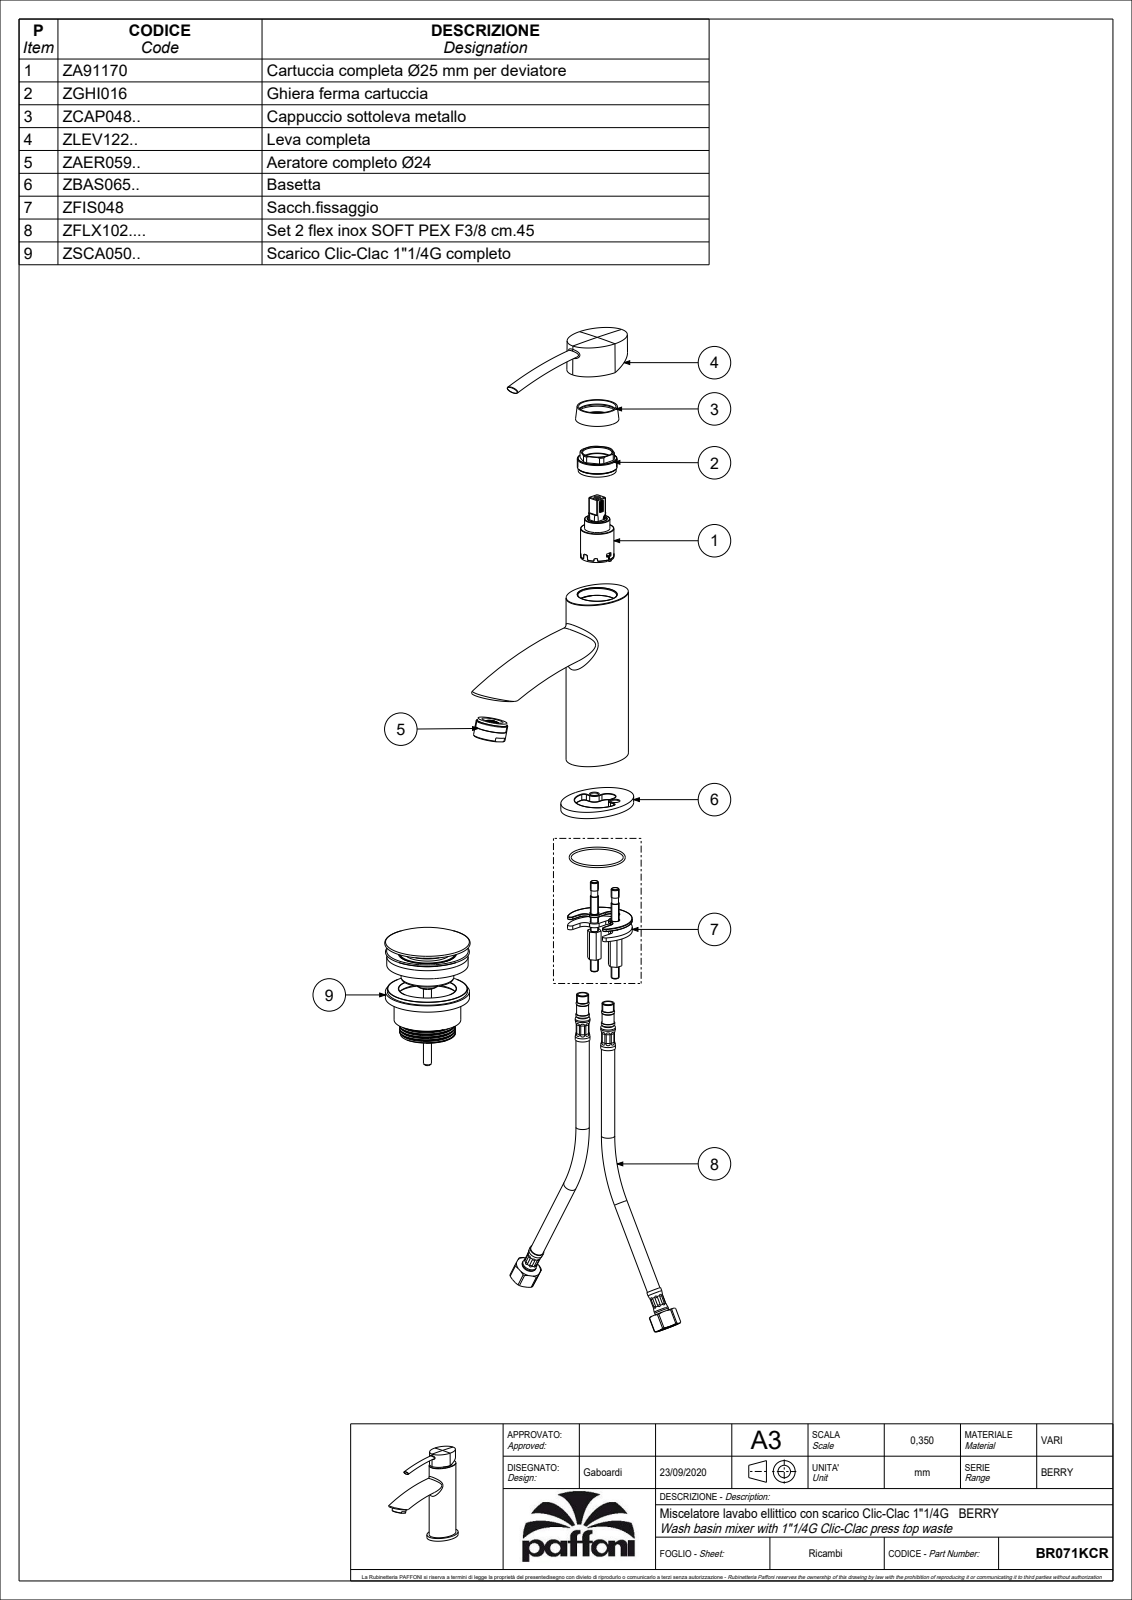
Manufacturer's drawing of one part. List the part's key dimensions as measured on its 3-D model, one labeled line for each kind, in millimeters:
Part name (STEP PRODUCT): BR071CR
STEP written by: CREO PARAMETRIC BY PTC INC, 2020044 (CONFIG_CONTROL_DESIGN)
Units: millimetres
Bodies: 2 solids, 2611 faces (1942 planar, 323 cylindrical, 346 other)
Overall size (bounding box): 159.2 × 158.34 × 46
Volume: 150 594 mm³ · Surface area: 87 583 mm²
Round holes (diameter × count): ⌀7 ×3, ⌀3 ×2, ⌀5 ×2, ⌀5.5 ×2, ⌀6.2 ×2, ⌀8.6 ×2, ⌀9.4 ×2, ⌀20 ×2, ⌀4.5 ×1, ⌀5.3 ×1, ⌀15 ×1, ⌀16 ×1
Round bosses / shafts (diameter × count): ⌀38.8 ×1, ⌀28.7 ×1, ⌀28.5 ×1, ⌀27 ×1, ⌀26 ×1, ⌀25 ×1, ⌀24.2 ×1, ⌀24 ×1
Partial cylindrical surfaces — rounded edges, fillets, slot ends (radius × count): R0.5 ×40, R0.3 ×23, R1 ×16, R0.2 ×13, R0.15 ×10, R2 ×10, R1.5 ×8, R1.25 ×4
Main face-to-face distances: 5, 156.9, 90.5, 151.9, 1, 102.5, 134, 129, 22.9, 12
Hole centre spacings: 7.5, 11, 11.24, 11.4, 13.46, 13.6, 13.87, 21.1
